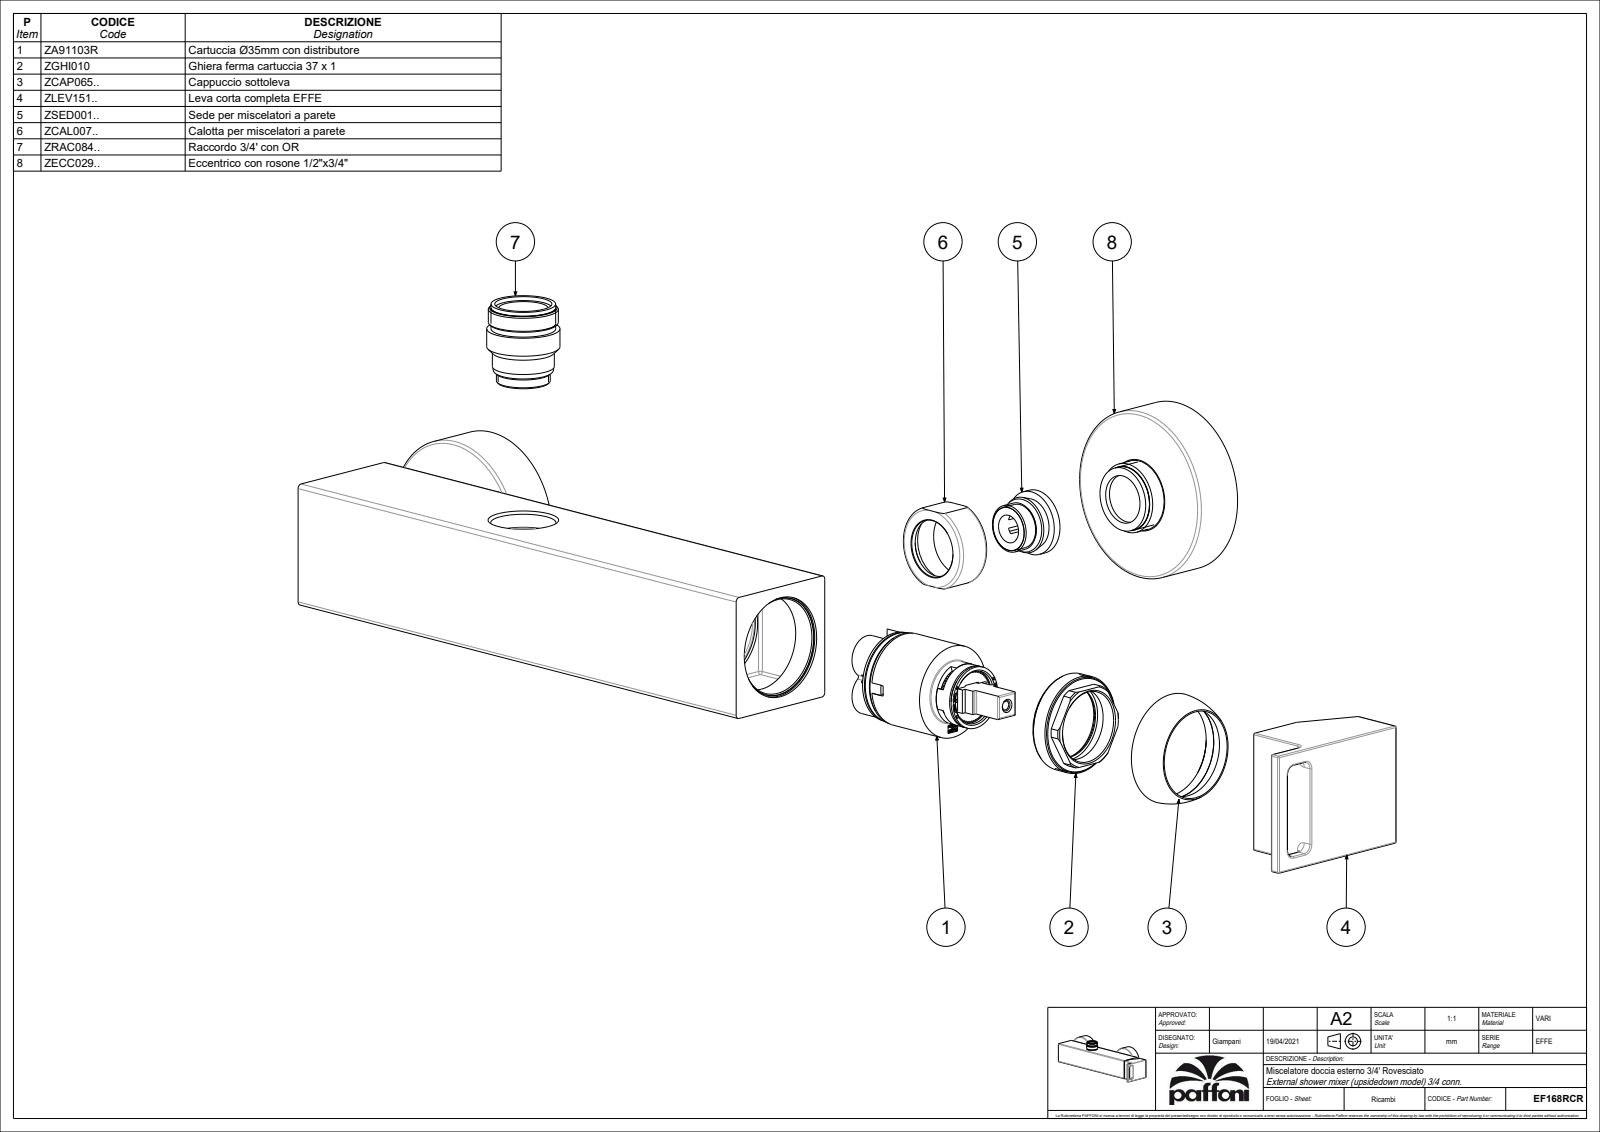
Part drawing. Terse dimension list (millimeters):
name: EF168RCR
written by: CREO PARAMETRIC BY PTC INC, 2020044 (CONFIG_CONTROL_DESIGN)
unit: mm
bodies: 1 solid, 1579 faces (772 planar, 480 cylindrical, 327 other)
size: 272.75 × 97.75 × 73
volume: 257 000 mm³; area: 170 815 mm²
holes: 3× ⌀9, 3× ⌀10.5, 3× ⌀12, 2× ⌀4, 2× ⌀7, 2× ⌀8, 2× ⌀18, 2× ⌀21.6, 2× ⌀24.5, 2× ⌀25, 2× ⌀37, 2× ⌀62.3
bosses: 3× ⌀24, 2× ⌀63.5, 2× ⌀27, 2× ⌀23.5, 2× ⌀17.7, 1× ⌀35, 1× ⌀34.8, 1× ⌀33.8
rounds: 90× R1, 60× R0.5, 11× R0.15, 9× R0.3, 5× R3, 4× R1.5, 4× R7, 2× R4.5
face distances: 42.75, 3.75, 46.5, 39, 3, 15, 18.75, 0.75, 61.5, 42
hole spacings: 0.71, 8.51, 8.6, 13.04, 13.21, 13.51, 6, 9.5
